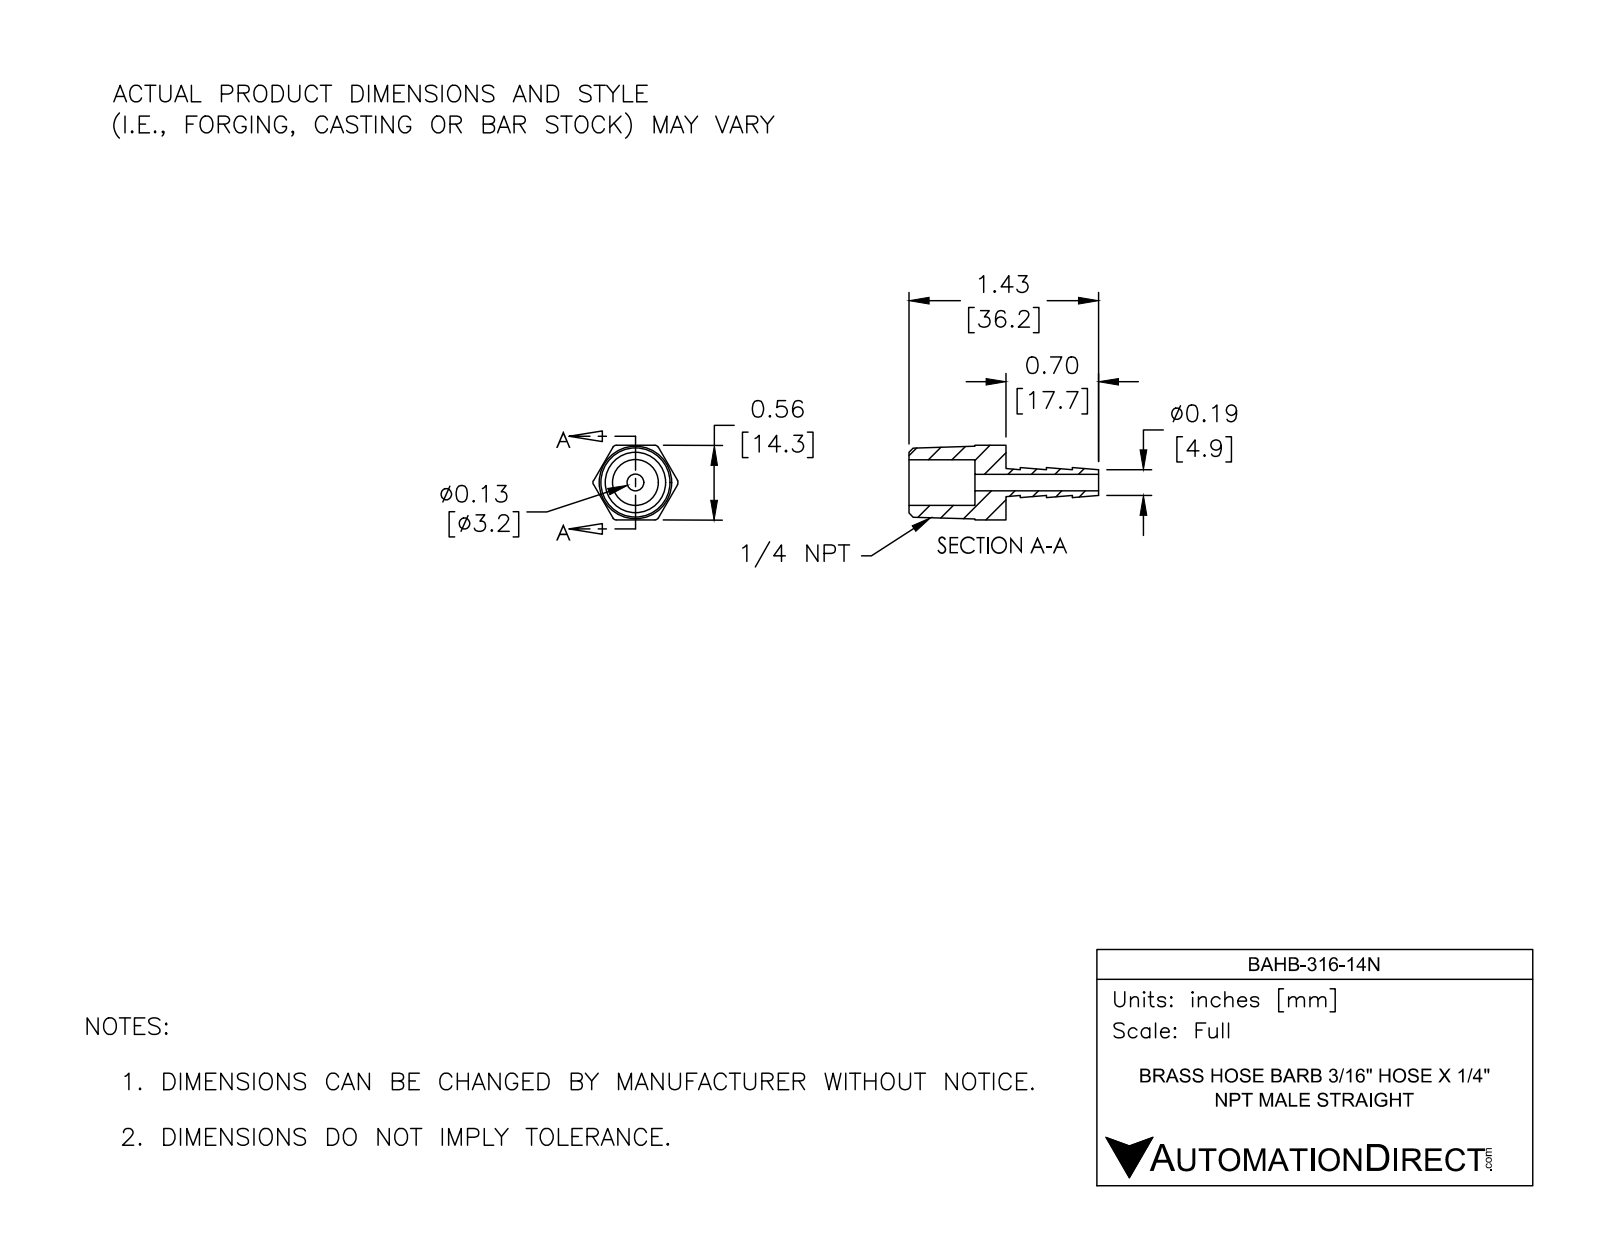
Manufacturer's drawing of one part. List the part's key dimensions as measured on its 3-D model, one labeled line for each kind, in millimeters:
Part name (STEP PRODUCT): BAHB-316-14N
STEP written by: SolidWorks 2017 (AUTOMOTIVE_DESIGN)
Units: millimetres
Bodies: 1 solid, 36 faces (14 planar, 10 cylindrical, 12 other)
Overall size (bounding box): 36.2 × 16.3 × 14.3
Volume: 2 290 mm³ · Surface area: 2 021 mm²
Round holes (diameter × count): ⌀3.2 ×1, ⌀8.7 ×1
Partial cylindrical surfaces — rounded edges, fillets, slot ends (radius × count): R0.8 ×6
Main face-to-face distances: 14.3, 5.9, 18.5, 12.6, 5, 17.7, 23.6, 36.2, 10, 14.9
